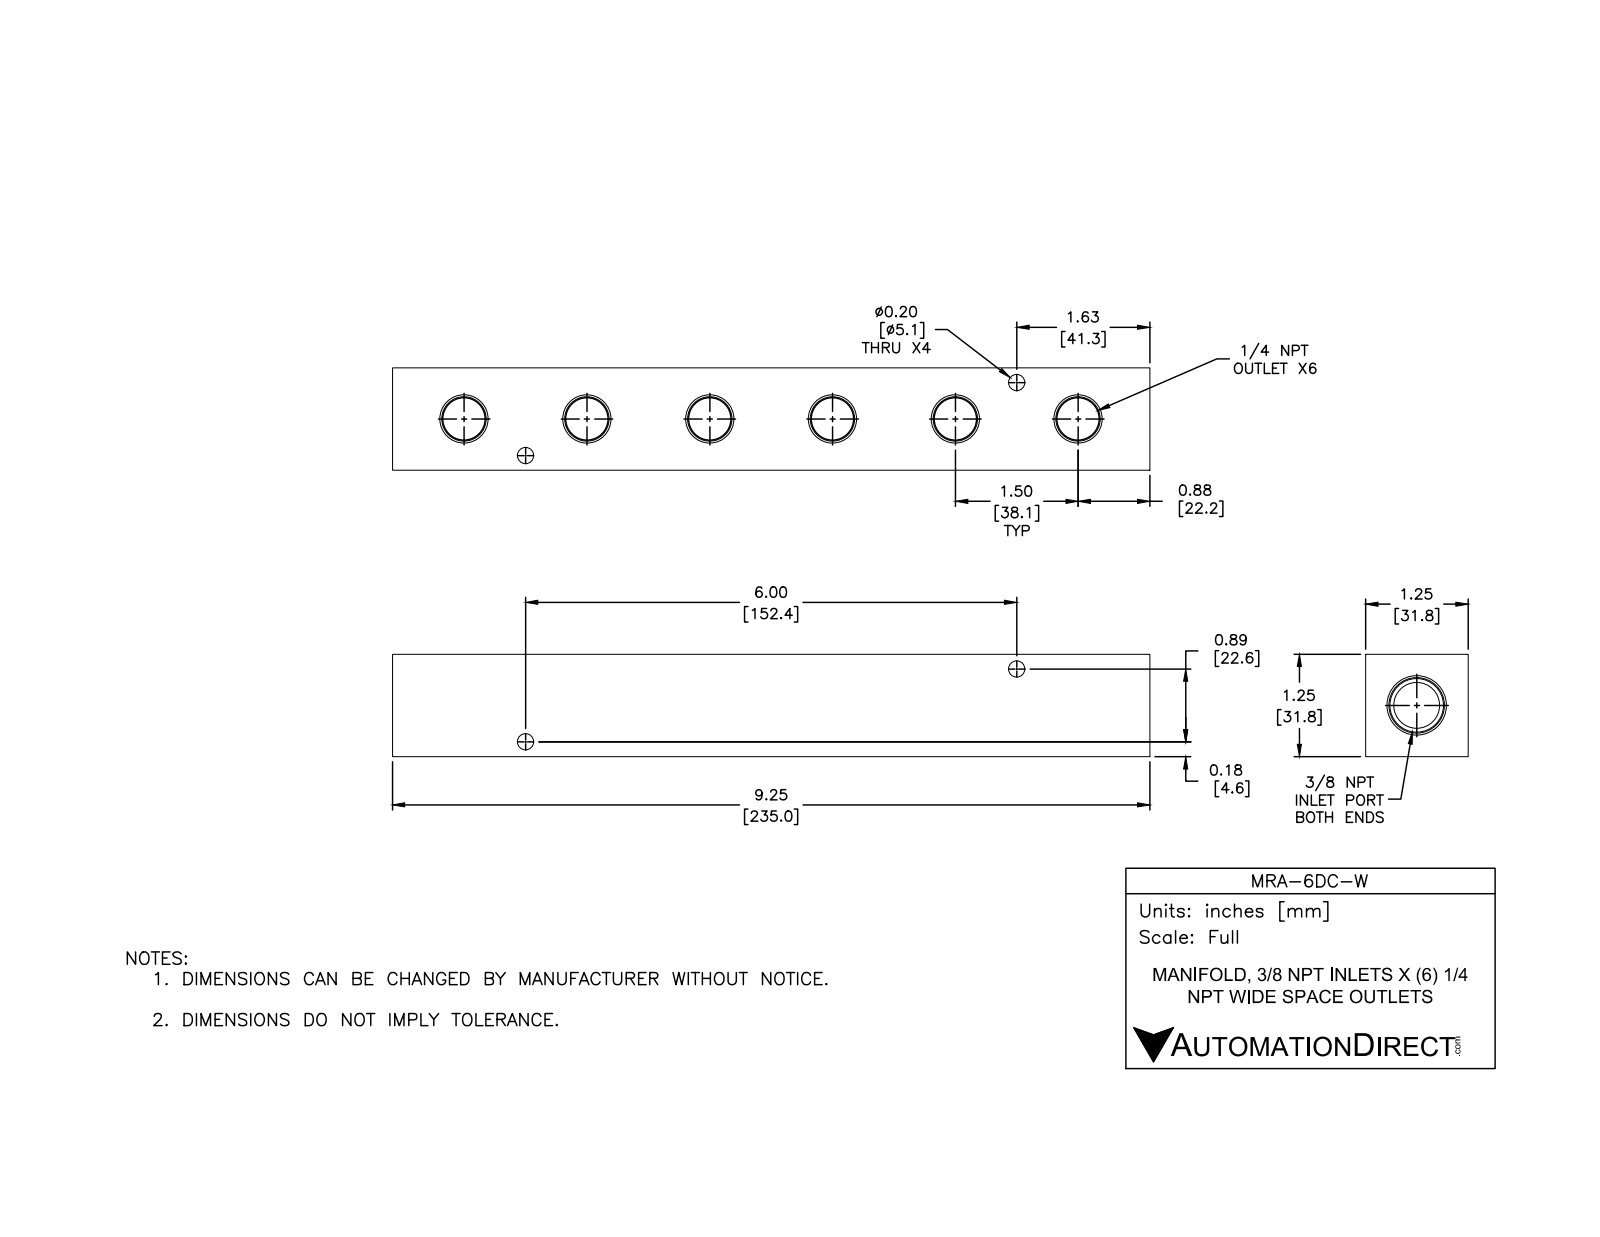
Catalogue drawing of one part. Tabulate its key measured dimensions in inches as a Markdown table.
| quantity | value |
| --- | --- |
| part name | MRA-6DC-W |
| STEP written by | SolidWorks 2015 (CONFIG_CONTROL_DESIGN) |
| units | inches |
| bodies | 1 solid, 82 faces (20 planar, 30 cylindrical, 32 other) |
| overall size | 9.25 × 1.25 × 1.25 |
| volume | 11.44 in³ |
| surface area | 69.37 in² |
| round holes (diameter × count) | 0.2 × 4, 0.562 × 1 |
| partial cylindrical surfaces (radius × count) | 0.219 × 6 |
| main face-to-face distances | 1.25, 9.25, 0.86, 0.39, 0.41, 8.84, 8.43 |
| hole center spacings | 6.066 |
